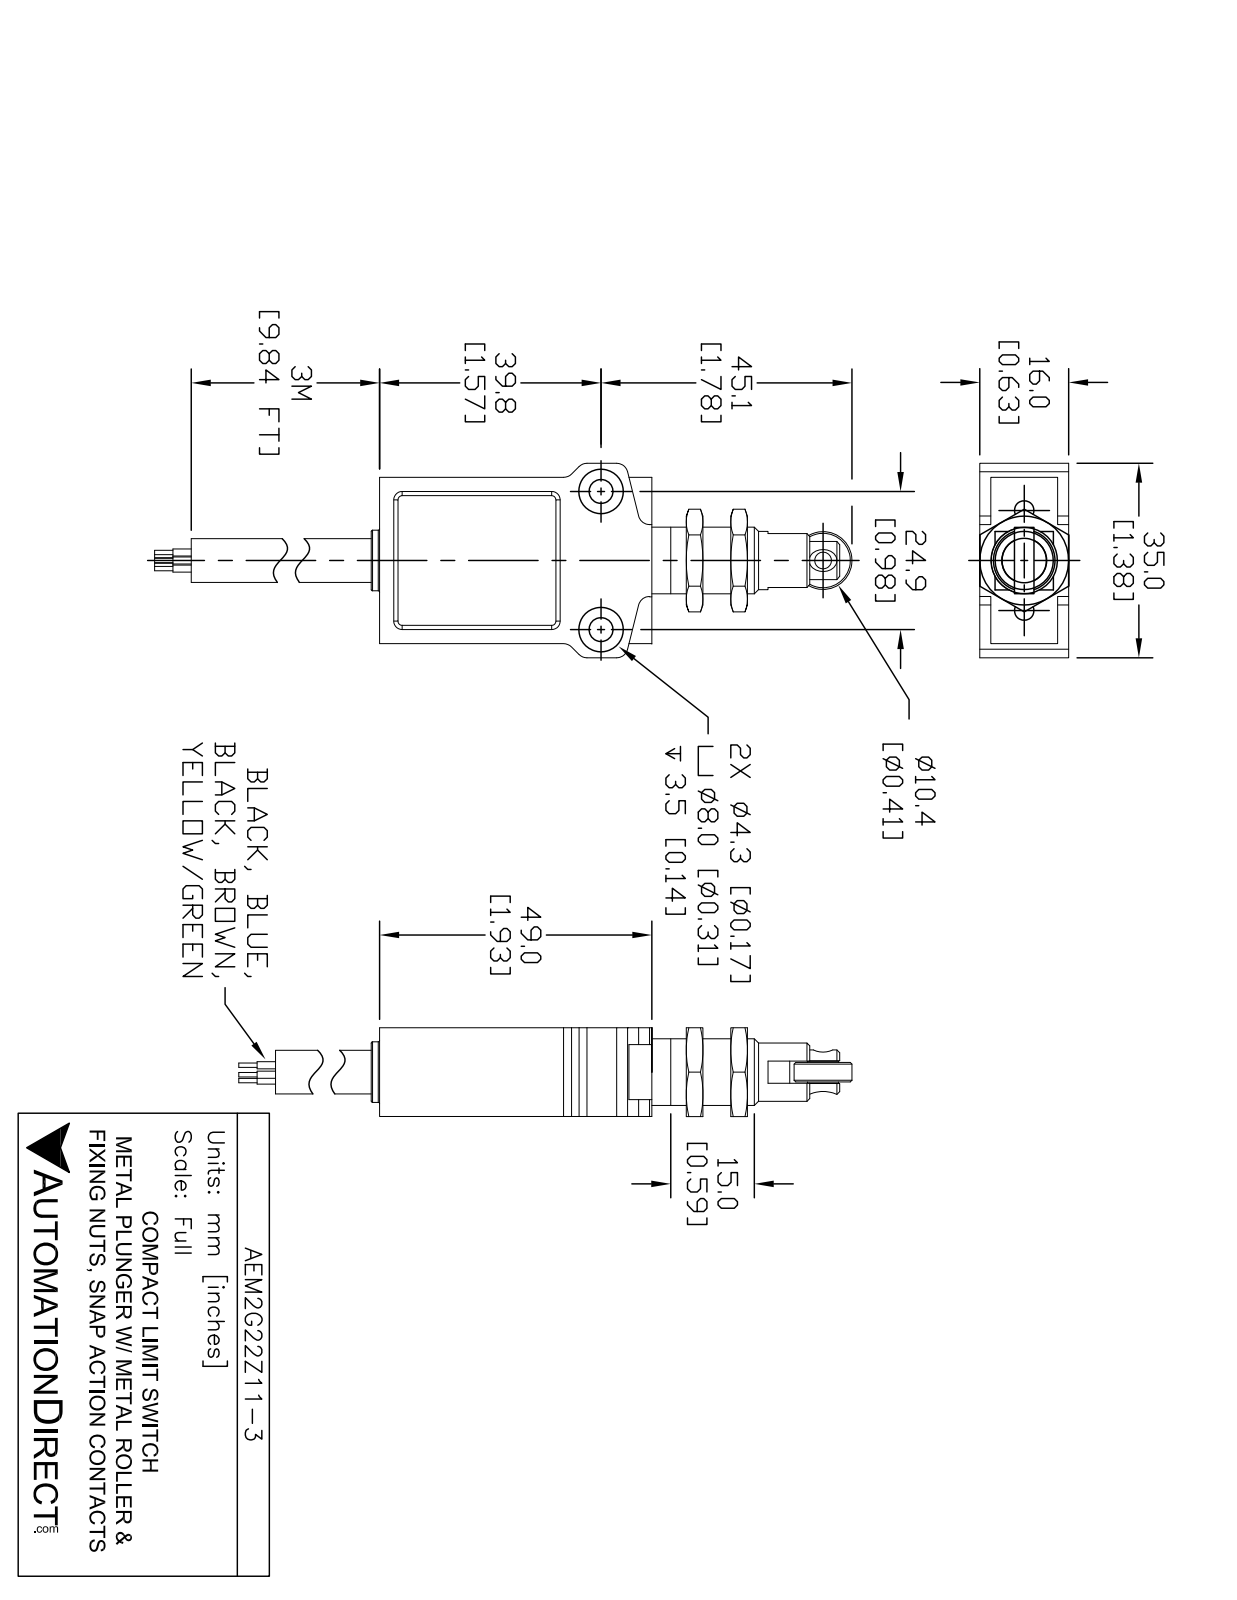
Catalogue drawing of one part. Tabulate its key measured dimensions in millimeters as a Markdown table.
| quantity | value |
| --- | --- |
| part name | AEM2G22Z11-3_Default |
| STEP written by | SolidWorks 2021 (CONFIG_CONTROL_DESIGN) |
| units | millimeters |
| bodies | 2 solids, 191 faces (98 planar, 47 cylindrical, 46 other) |
| overall size | 100.7 × 35.1 × 16 |
| volume | 25 650 mm³ |
| surface area | 9 052 mm² |
| round holes (diameter × count) | 4.5 × 2, 8.7 × 2 |
| round bosses / shafts (diameter × count) | 1.3 × 5, 0.8 × 5, 10.4 × 2, 11.9 × 1, 10.9 × 1, 7.9 × 1 |
| partial cylindrical surfaces (radius × count) | 0.8 × 8, 2 × 8, 3.4 × 1 |
| main face-to-face distances | 0.8, 15.2, 14.5, 16, 30, 3, 7.6, 49, 4.7, 11.3 |
| hole center spacings | 24.9 |
